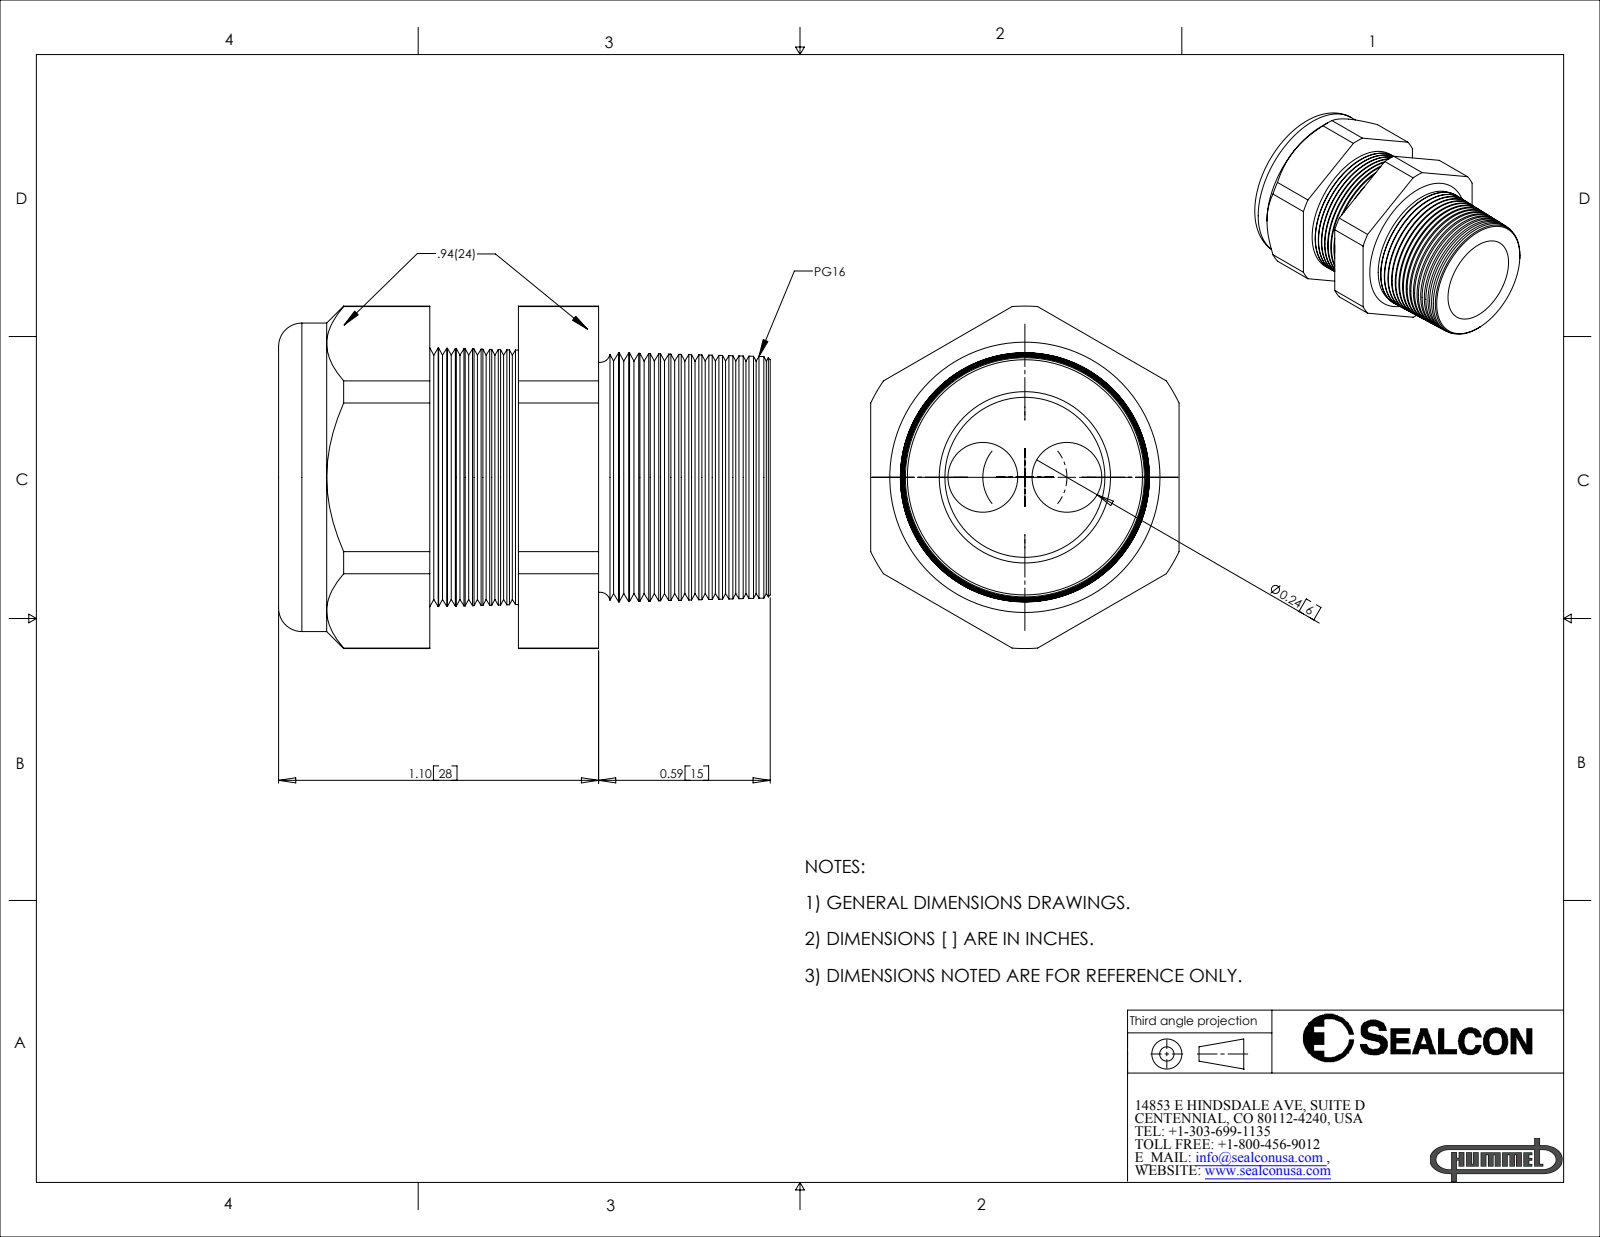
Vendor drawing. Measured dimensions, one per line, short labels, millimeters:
name: CD16A6-GY
written by: SolidWorks 2007 (CONFIG_CONTROL_DESIGN)
unit: mm
bodies: 2 solids, 180 faces (20 planar, 24 cylindrical, 136 other)
size: 37.8 × 29.9 × 26.9
volume: 13 100 mm³; area: 7 800 mm²
holes: 2× ⌀6.1, 1× ⌀13.5, 1× ⌀14
bosses: 1× ⌀26.9
rounds: 1× R14.9
face distances: 26.9, 20.9, 13.2, 7.7, 27.9, 14.7, 7, 37.8, 24.6, 16.9
hole spacings: 3.7, 7.3
